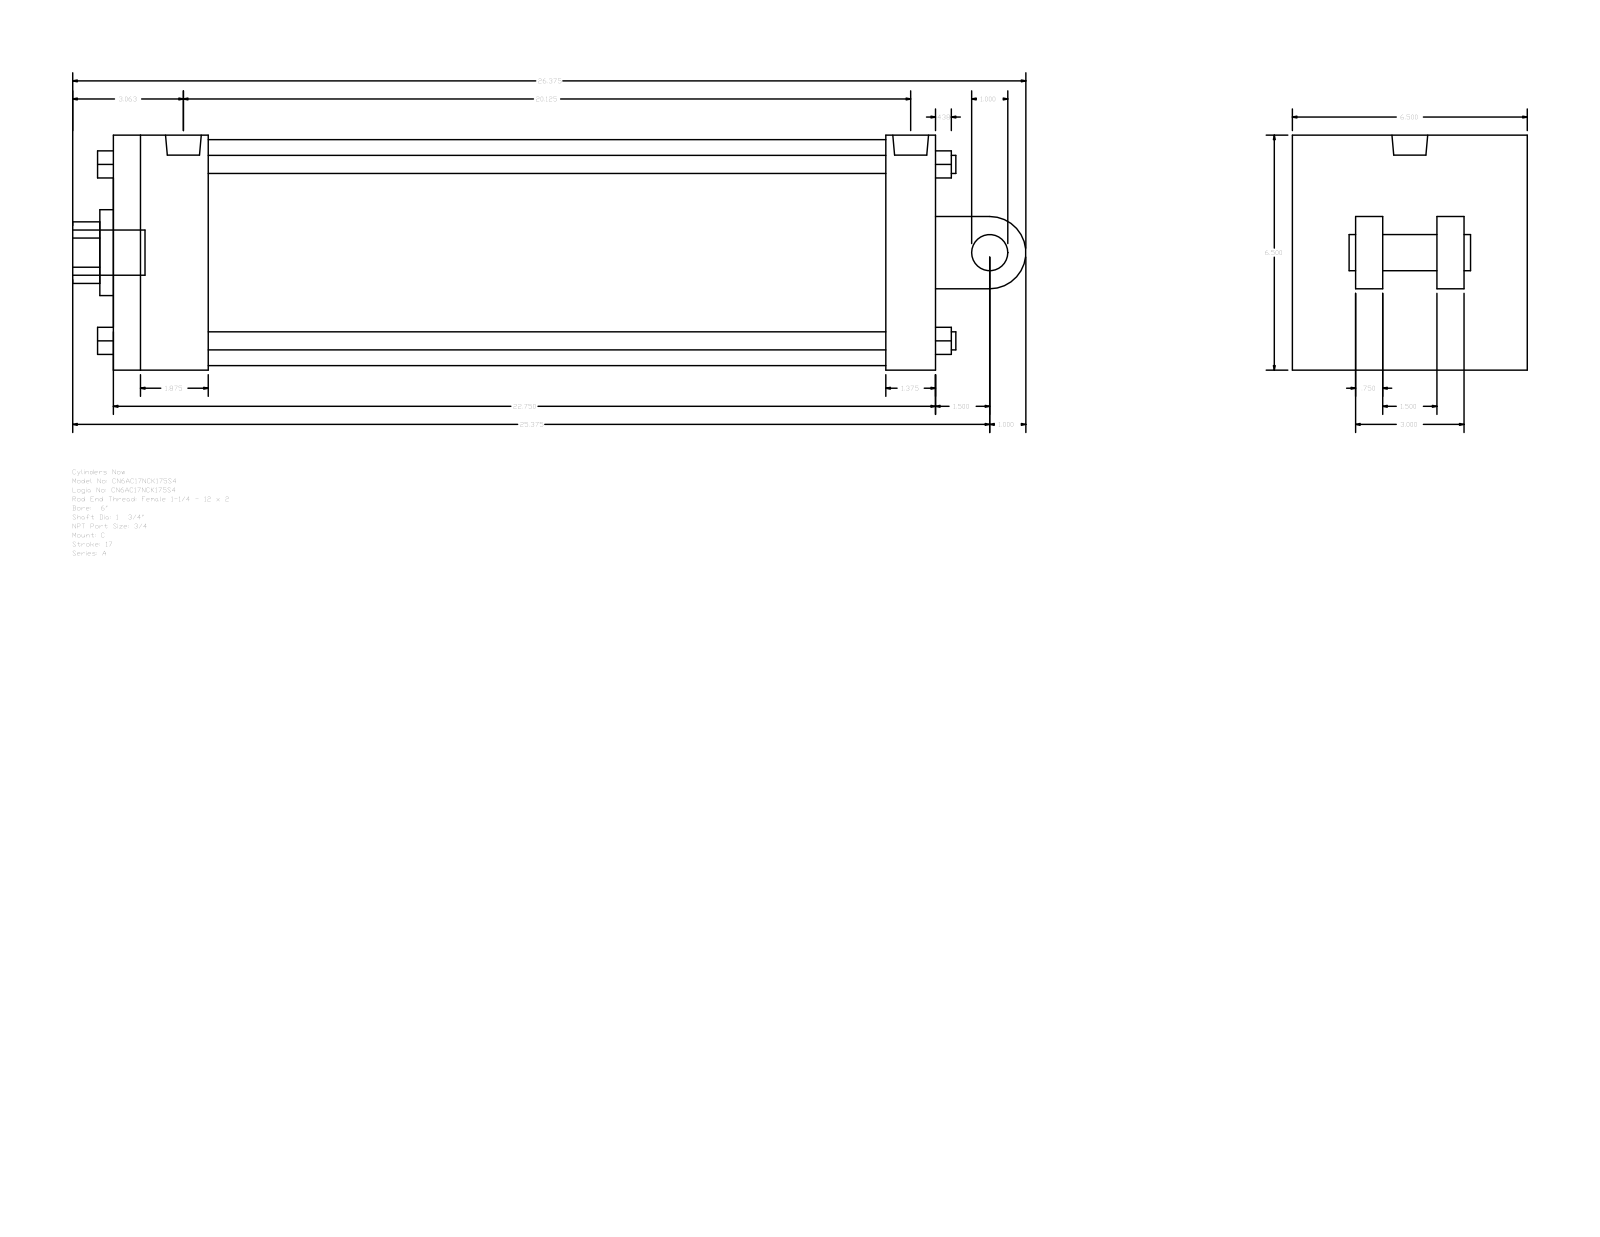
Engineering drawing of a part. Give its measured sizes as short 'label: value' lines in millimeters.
name: A_C__0600_1.75
written by: GSSL Pune (CONFIG_CONTROL_DESIGN)
unit: mm
bodies: 0 solids, 135 faces (102 planar, 33 cylindrical, 0 other)
size: 669.92 × 165.1 × 165.1
holes: 2× ⌀15.08, 1× ⌀25.12, 1× ⌀44.45, 1× ⌀60.33, 1× ⌀158.75
bosses: 4× ⌀12.7, 2× ⌀15.08, 1× ⌀31.75, 1× ⌀25.4, 1× ⌀25.12
rounds: 1× R21.63, 1× R25.4
face distances: 165.1, 577.85, 19.05, 57.15, 34.92, 66.68, 511.17, 542.93, 476.25, 44.45
hole spacings: 5.56
